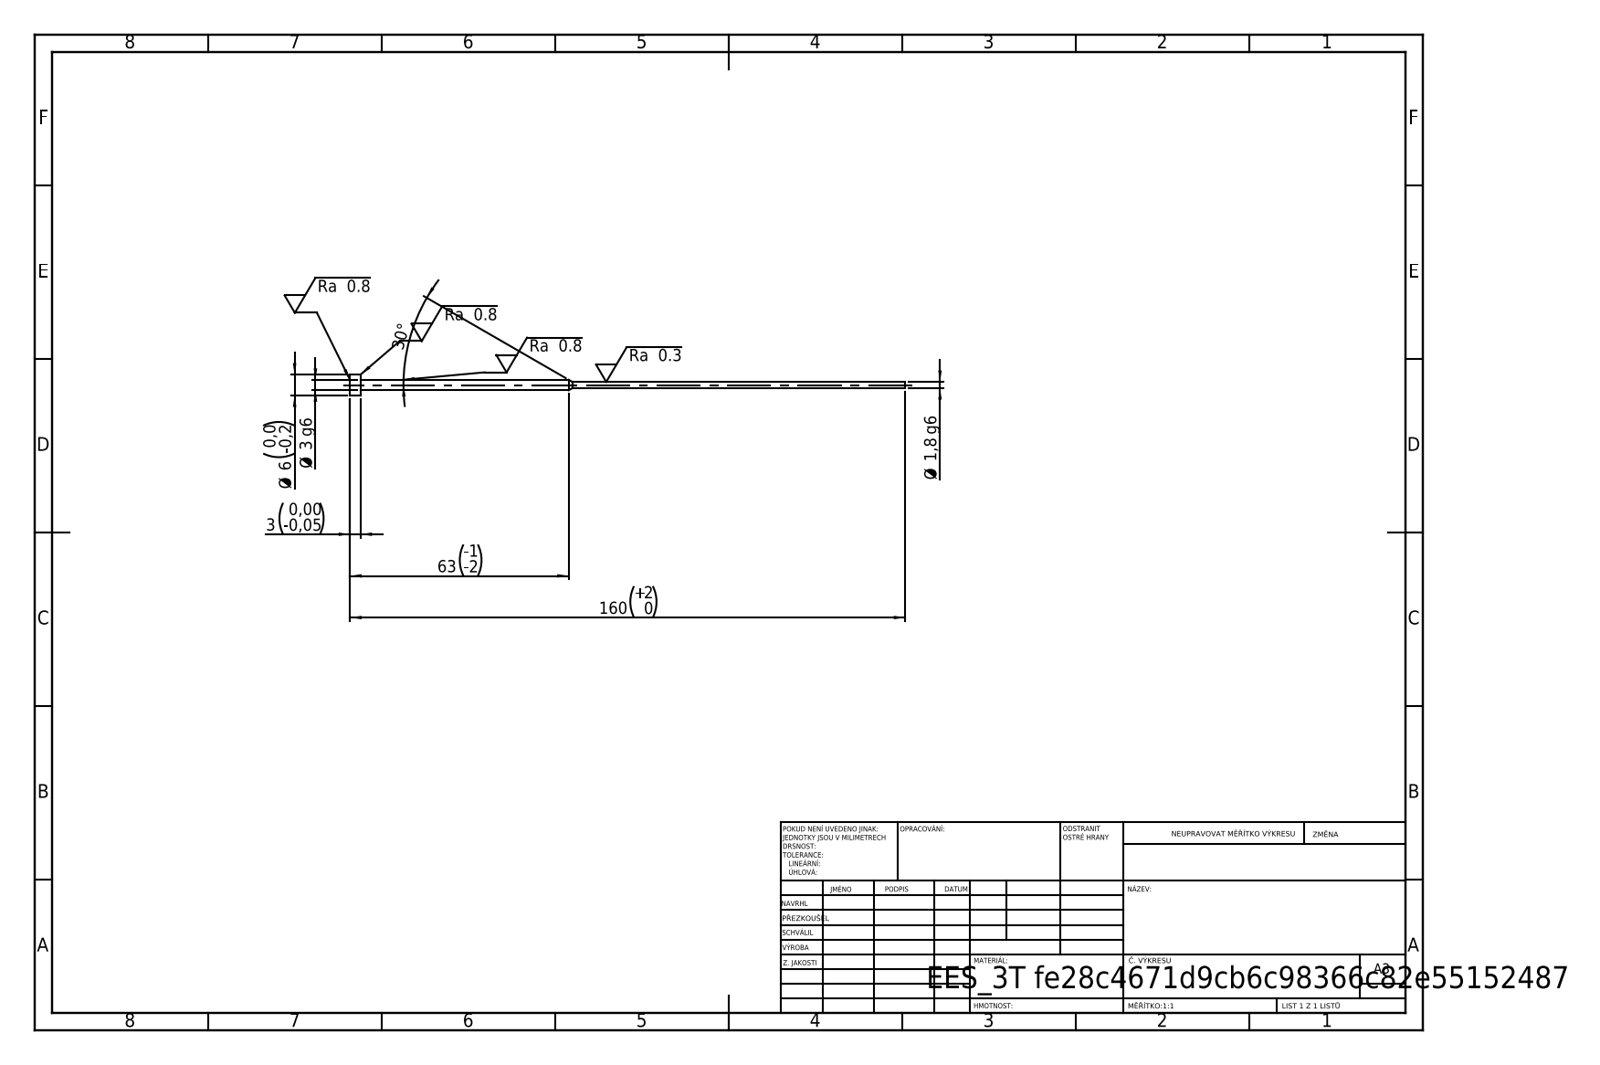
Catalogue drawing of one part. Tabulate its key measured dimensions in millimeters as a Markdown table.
| quantity | value |
| --- | --- |
| STEP written by | SolidWorks 2019 (CONFIG_CONTROL_DESIGN) |
| units | millimeters |
| bodies | 1 solid, 11 faces (3 planar, 6 cylindrical, 2 other) |
| overall size | 160 × 6 × 6 |
| volume | 758 mm³ |
| surface area | 1 226 mm² |
| round bosses / shafts (diameter × count) | 6 × 1, 3 × 1, 1.8 × 1 |
| main face-to-face distances | 3, 157, 160 |
